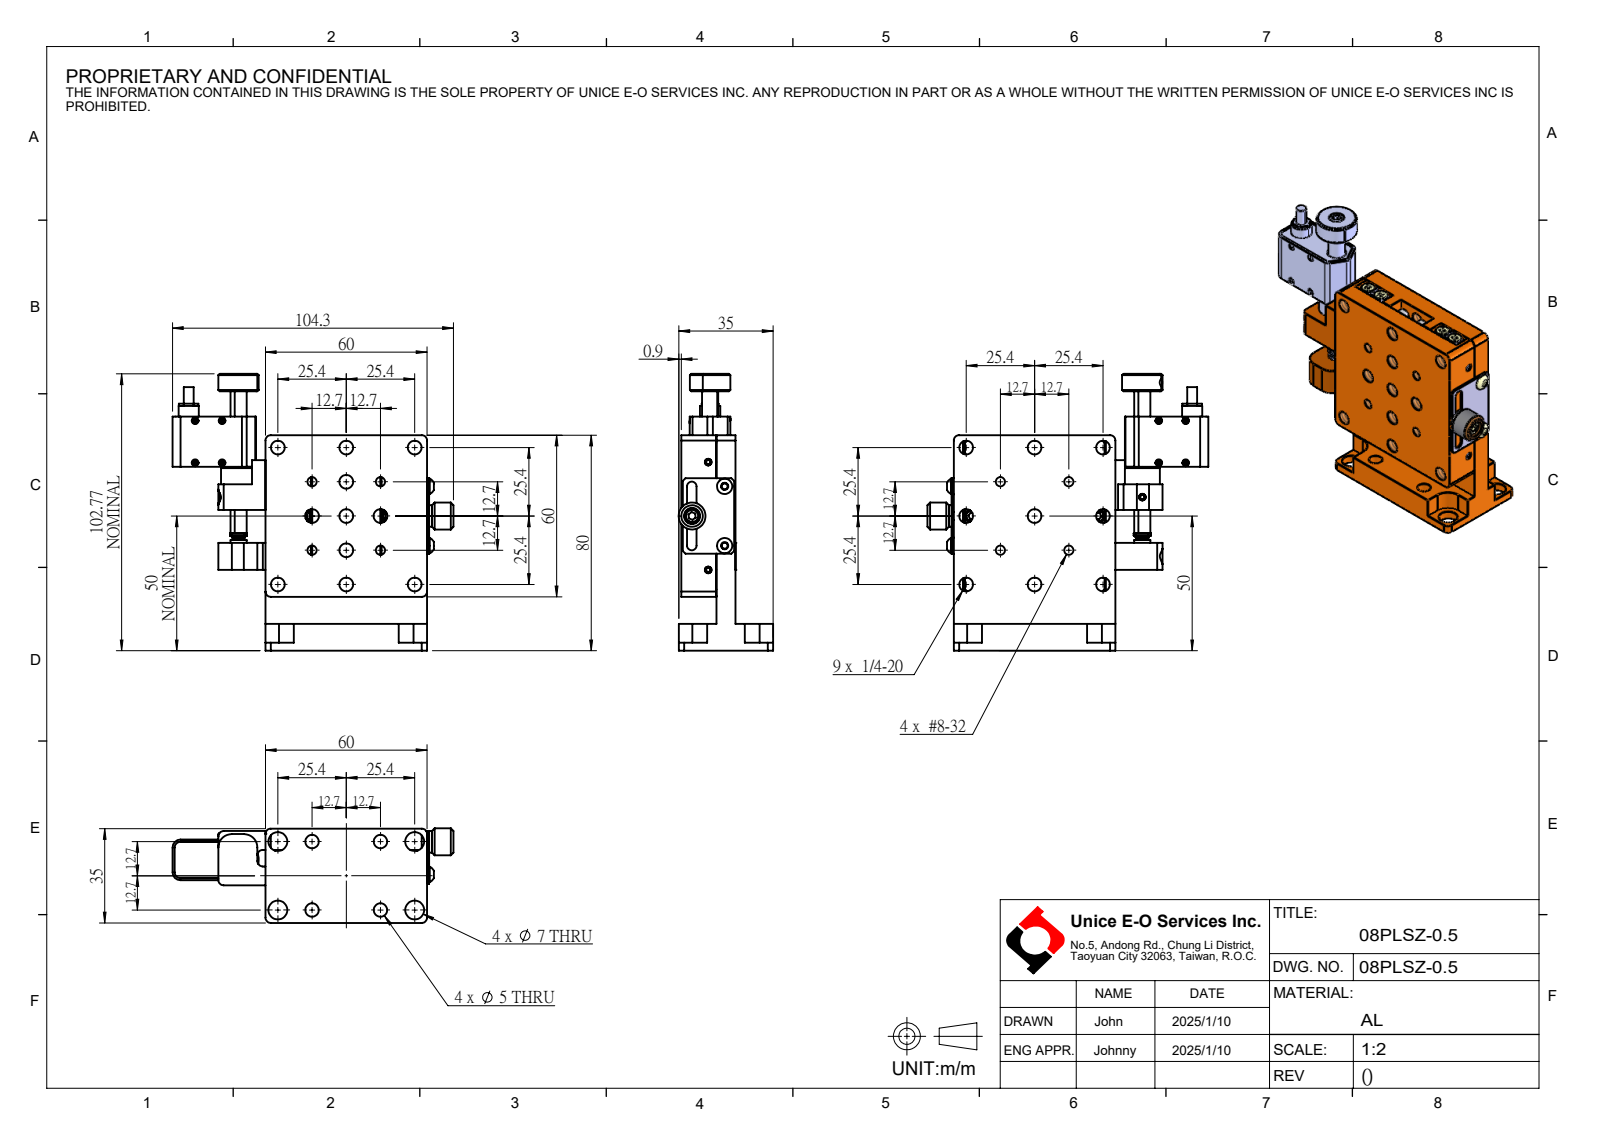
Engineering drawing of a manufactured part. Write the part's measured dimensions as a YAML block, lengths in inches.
part_name: "08PLSZ-0.5"
step_written_by: "SolidWorks 2024 (CONFIG_CONTROL_DESIGN)"
units: inches
bodies: {solids: 0, faces: 1519, planar: 763, cylindrical: 459, other: 297}
overall_size: [4.106, 4.046, 1.382]
round_holes:
  - {diameter: 0.081, count: 20}
  - {diameter: 0.197, count: 17}
  - {diameter: 0.098, count: 16}
  - {diameter: 0.118, count: 13}
  - {diameter: 0.201, count: 13}
  - {diameter: 0.136, count: 4}
  - {diameter: 0.276, count: 4}
  - {diameter: 0.134, count: 3}
  - {diameter: 0.256, count: 3}
  - {diameter: 0.055, count: 2}
  - {diameter: 0.079, count: 2}
  - {diameter: 0.126, count: 2}
round_bosses_or_shafts:
  - {diameter: 0.177, count: 16}
  - {diameter: 0.098, count: 16}
  - {diameter: 0.118, count: 9}
  - {diameter: 0.217, count: 4}
  - {diameter: 0.197, count: 4}
  - {diameter: 0.1, count: 4}
  - {diameter: 0.236, count: 3}
  - {diameter: 0.224, count: 2}
partial_cylinders:
  - {radius: 0.079, count: 15}
  - {radius: 0.197, count: 4}
  - {radius: 0.217, count: 4}
  - {radius: 0.069, count: 2}
  - {radius: 0.118, count: 2}
  - {radius: 0.098, count: 1}
face_to_face_distances: [0.276, 0.516, 0.24, 0.791, 0.394, 0.236, 0.272, 0.244, 0.52, 0.031]
hole_center_spacings: [1.118, 1, 0.5, 0.707, 1.581, 0.787, 1.414, 1.803]
